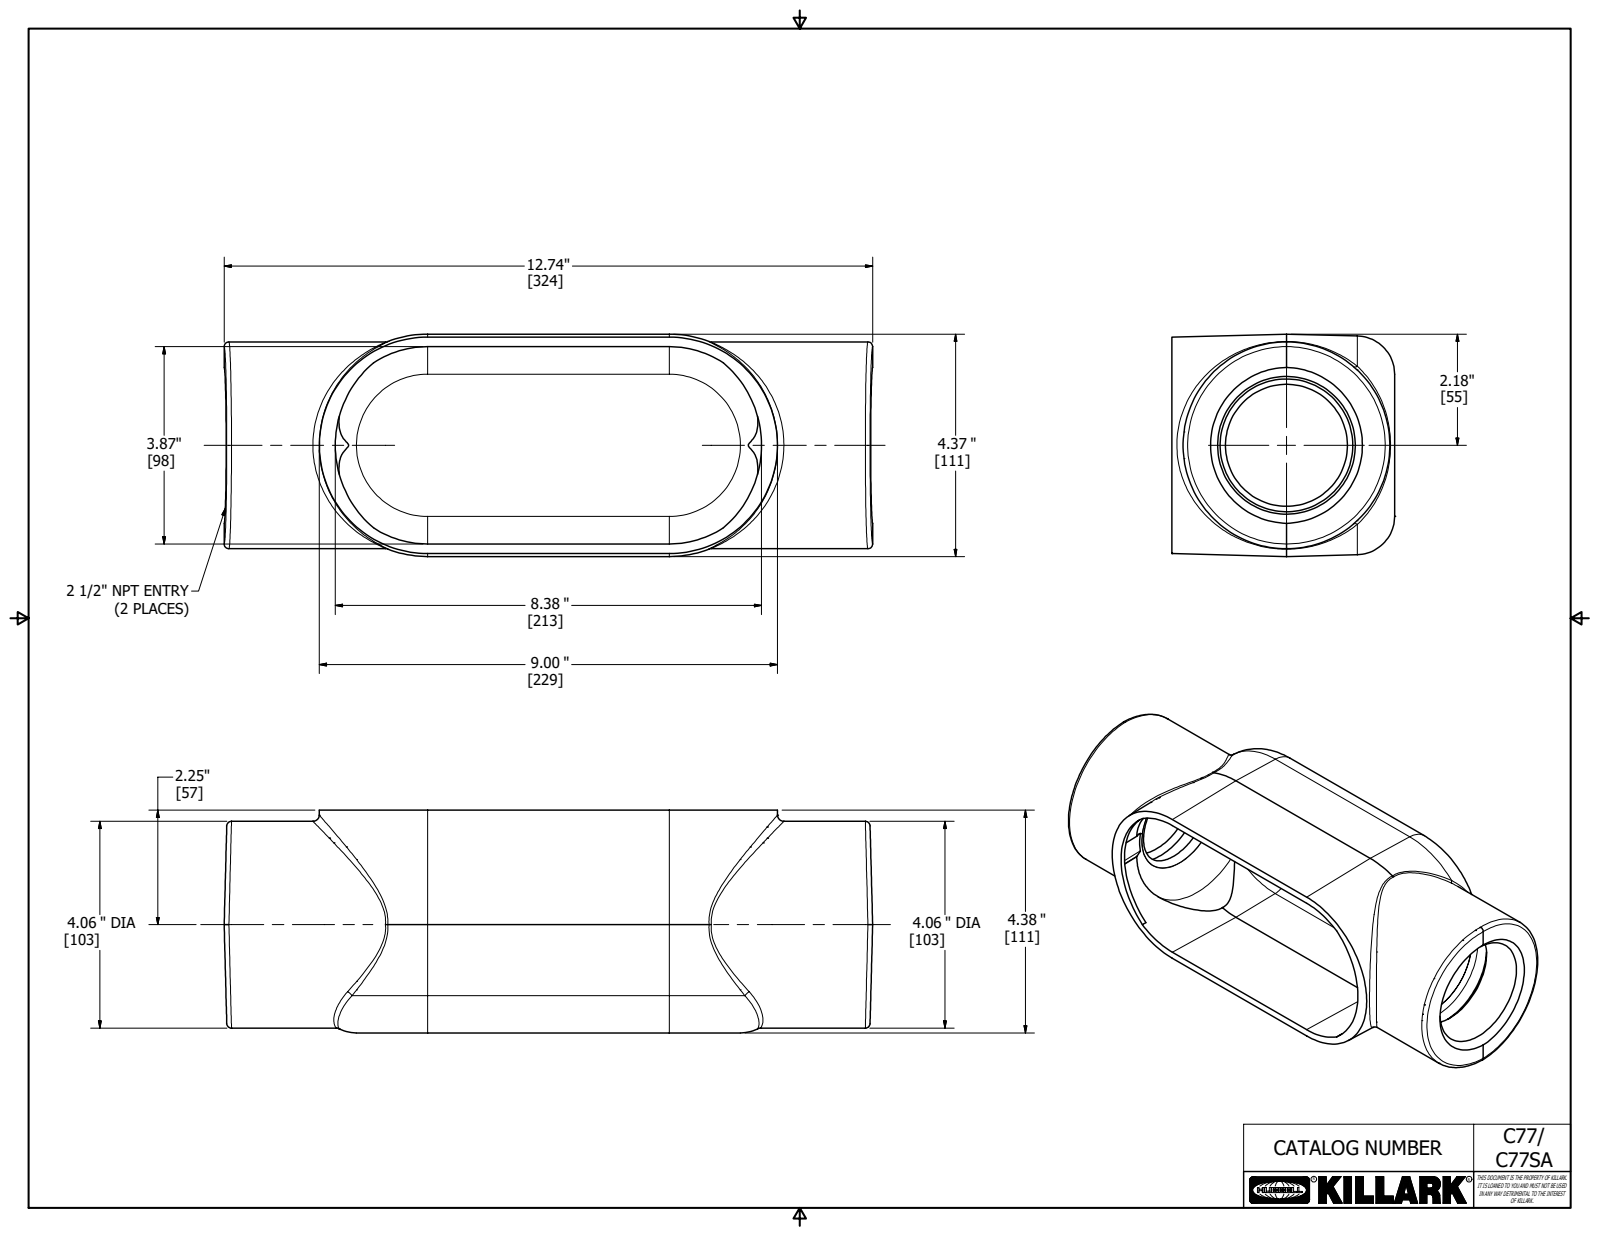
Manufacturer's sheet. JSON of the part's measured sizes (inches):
{"part_name": "17720", "step_written_by": "Autodesk Inventor 2018 (AUTOMOTIVE_DESIGN)", "units": "inches", "bodies": {"solids": 1, "faces": 96, "planar": 32, "cylindrical": 20, "other": 44}, "overall_size": [12.743, 4.375, 4.368], "volume_in3": 48.79, "surface_area_in2": 327.6, "round_holes": [[2.886, 1]], "round_bosses_or_shafts": [[4.062, 1]], "partial_cylinders_radius": [[0.05, 4], [0.125, 4], [0.562, 2], [0.75, 2], [1.937, 1]], "face_to_face_distances": [0.187, 4.18, 4.368, 3.993, 4.375, 4.187, 12.743, 0.031, 0.156, 4.344]}
